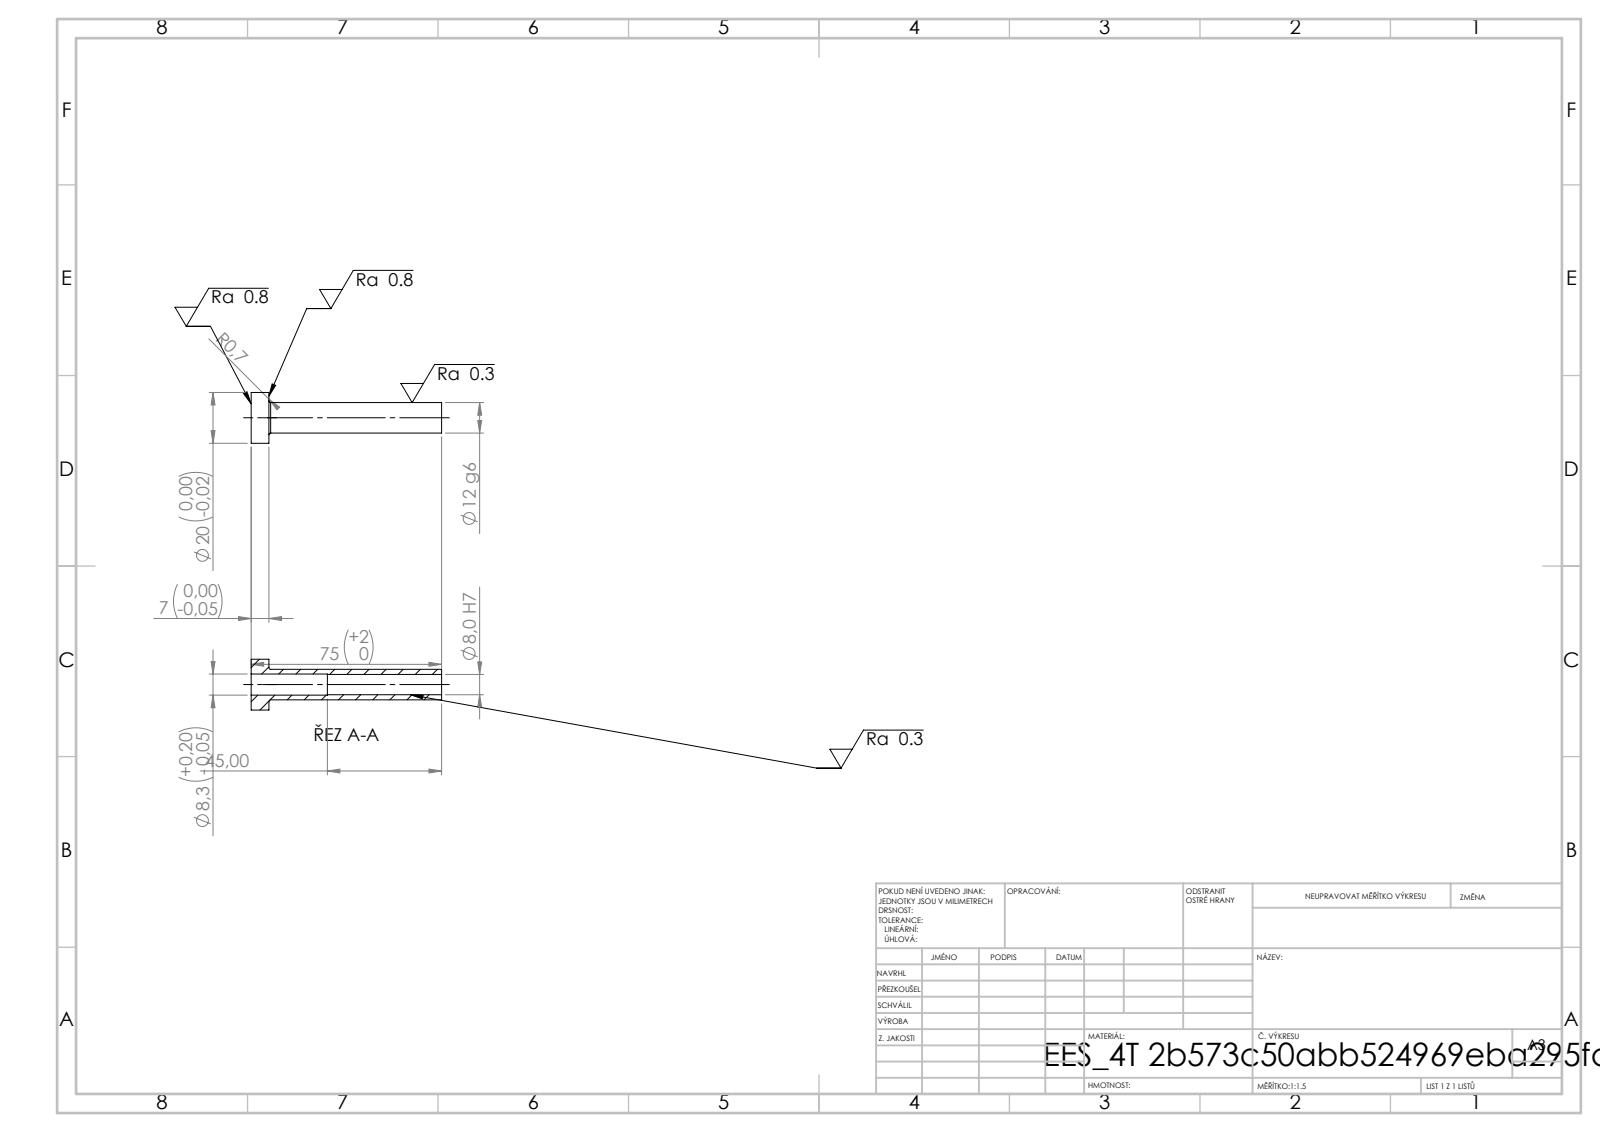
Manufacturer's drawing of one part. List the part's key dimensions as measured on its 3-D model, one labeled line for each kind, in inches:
STEP written by: SolidWorks 2019 (CONFIG_CONTROL_DESIGN)
Units: inches
Bodies: 1 solid, 14 faces (4 planar, 8 cylindrical, 2 other)
Overall size (bounding box): 2.953 × 0.787 × 0.787
Volume: 0.367 in³ · Surface area: 8.421 in²
Round holes (diameter × count): ⌀0.315 ×1, ⌀0.327 ×1
Round bosses / shafts (diameter × count): ⌀0.787 ×1, ⌀0.472 ×1
Main face-to-face distances: 0.276, 2.953, 2.677, 1.181, 0.906, 1.772
